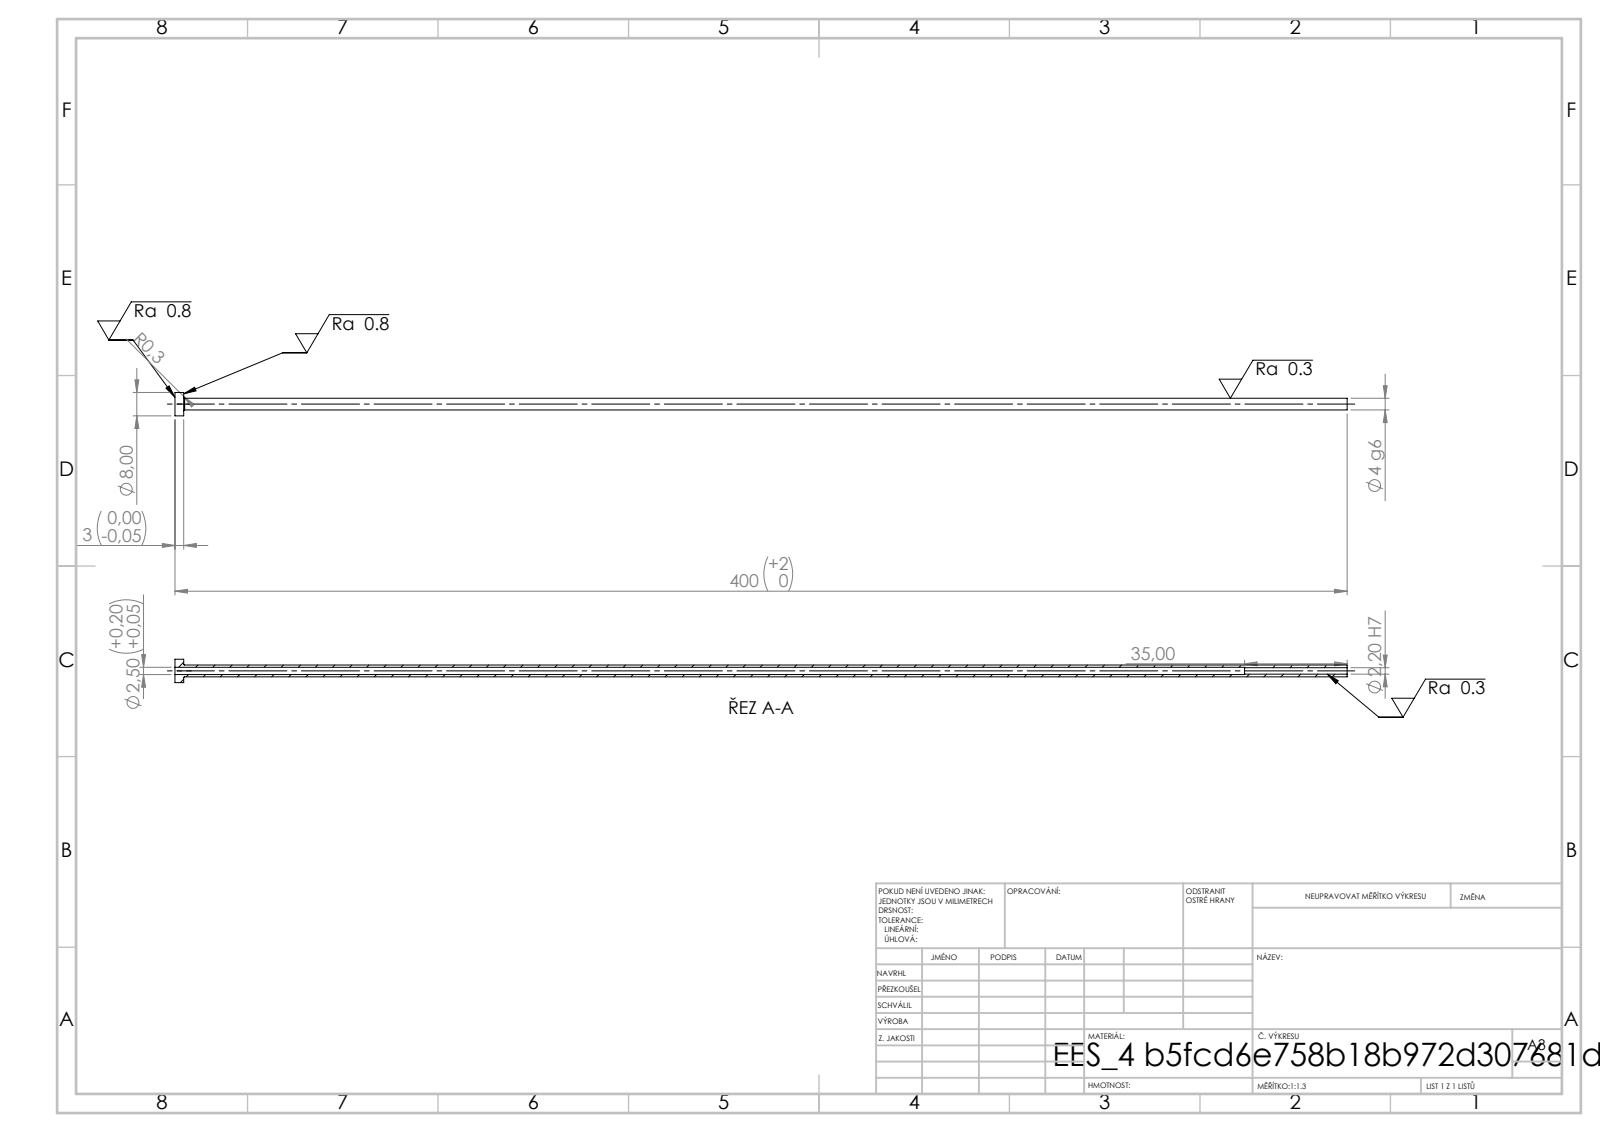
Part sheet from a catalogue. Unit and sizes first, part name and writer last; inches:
Units: inches
Overall size (bounding box): 15.748 × 0.315 × 0.315
Round holes (diameter × count): ⌀0.087 ×1, ⌀0.098 ×1
Round bosses / shafts (diameter × count): ⌀0.315 ×1, ⌀0.157 ×1
Main face-to-face distances: 0.118, 15.748, 15.63, 14.37, 14.252, 1.378
Volume: 0.196 in³ · Surface area: 12.81 in²
Bodies: 1 solid, 14 faces (4 planar, 8 cylindrical, 2 other)
STEP written by: SolidWorks 2019 (CONFIG_CONTROL_DESIGN)
